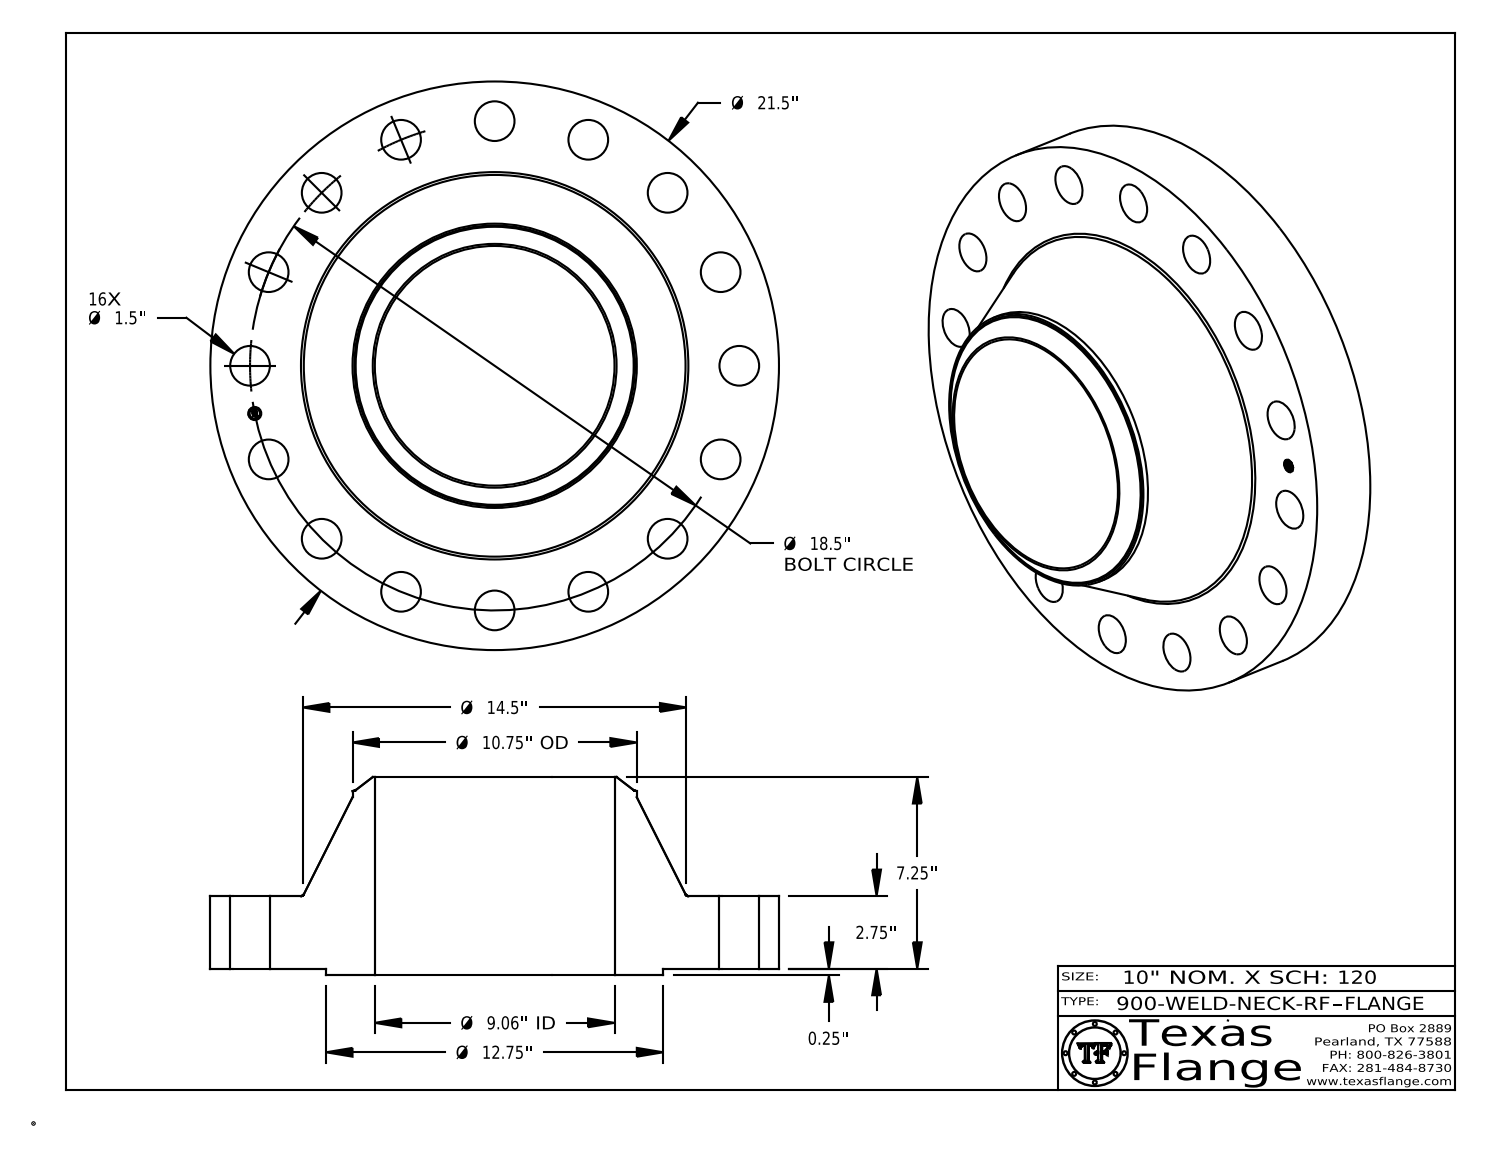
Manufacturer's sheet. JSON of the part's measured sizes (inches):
{"part_name": "900-WELD-NECK-RF", "step_written_by": "CATIA V5 STEP AP214 (AUTOMOTIVE_DESIGN)", "units": "inches", "bodies": {"solids": 1, "faces": 439, "planar": 369, "cylindrical": 60, "other": 10}, "overall_size": [21.5, 21.5, 7.5], "volume_in3": 1002, "surface_area_in2": 1261, "round_holes": [[1.5, 16], [0.495, 1], [9.062, 1]], "round_bosses_or_shafts": [[0.03, 8], [21.5, 1], [12.75, 1], [10.75, 1], [0.39, 1]], "face_to_face_distances": [2.75, 0.25, 3, 7.5, 7.25, 4.5, 2.985, 2.735, 0.015, 4.515], "hole_center_spacings": [15.382, 7.08, 9.25, 13.081, 3.609, 3.609, 10.278, 10.278]}
